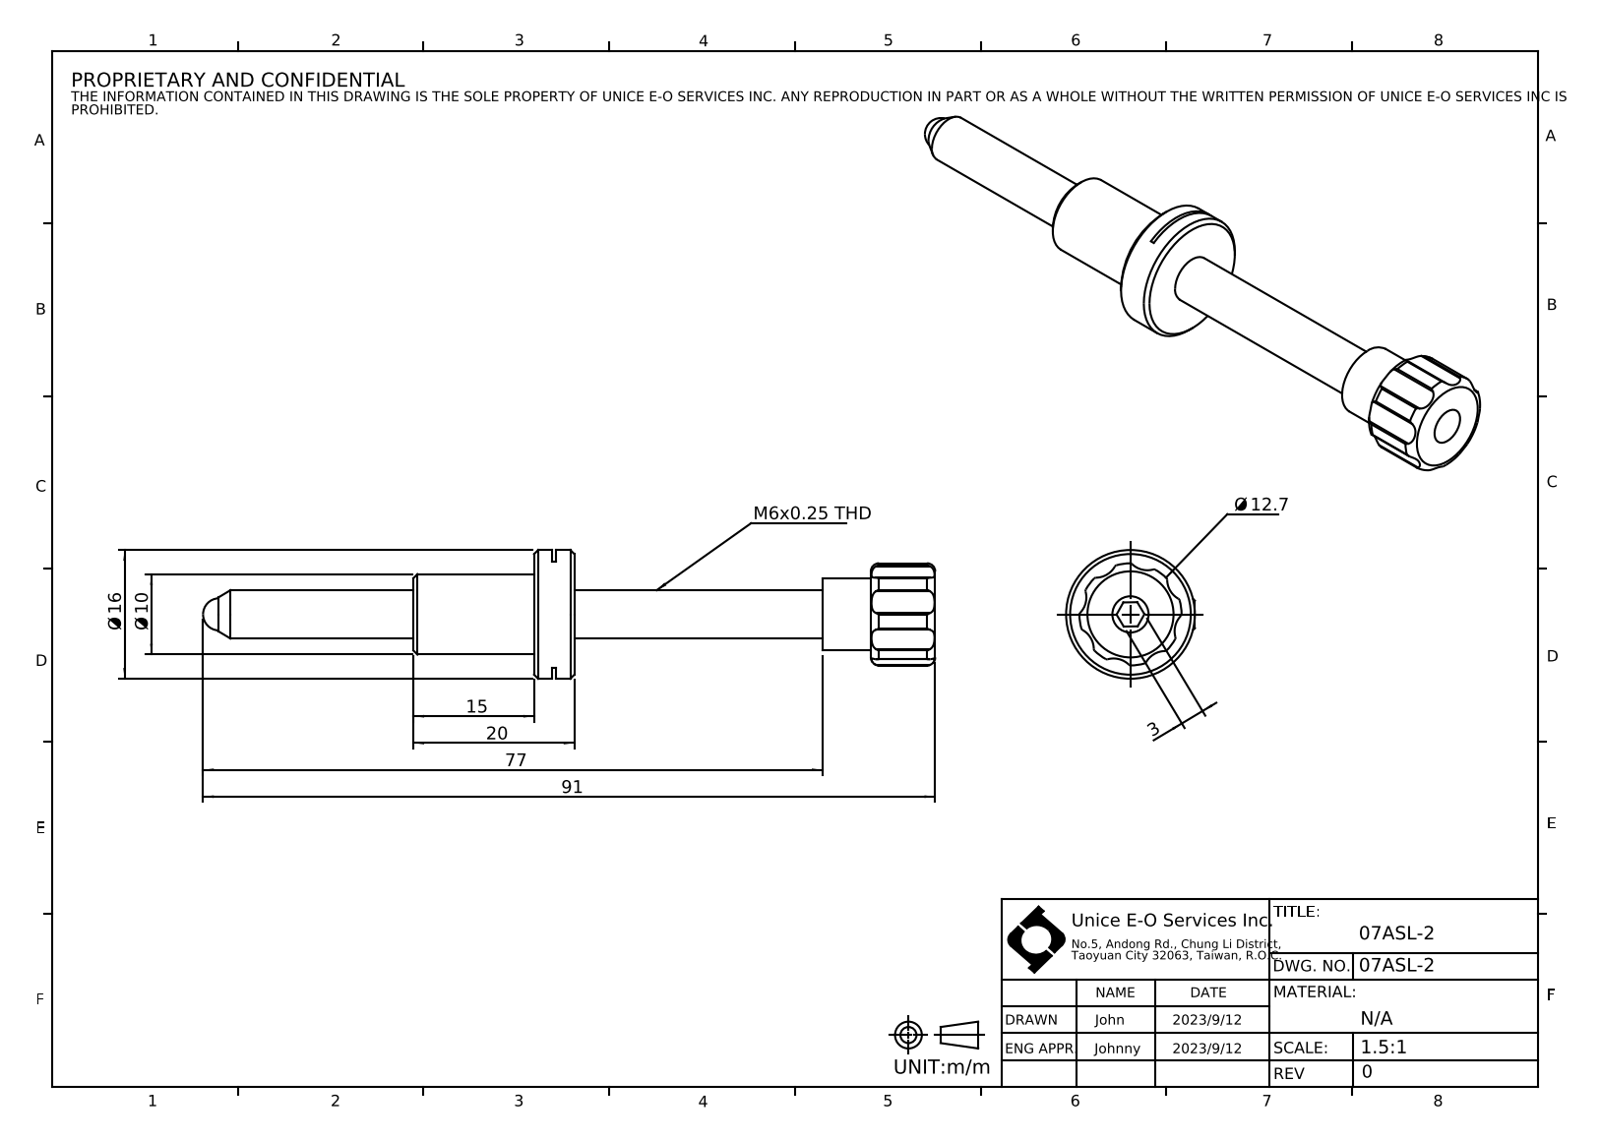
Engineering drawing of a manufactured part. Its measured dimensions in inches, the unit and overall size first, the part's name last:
Units: inches
Overall size (bounding box): 3.583 × 0.63 × 0.63
Round holes (diameter × count): ⌀0.177 ×1
Round bosses / shafts (diameter × count): ⌀0.63 ×1, ⌀0.394 ×1, ⌀0.354 ×1, ⌀0.236 ×1, ⌀0.157 ×1
Partial cylindrical surfaces — rounded edges, fillets, slot ends (radius × count): R0.012 ×16, R0.108 ×8, R0.25 ×1
Main face-to-face distances: 0.089, 0.108, 0.02, 0.197, 1.894, 1.805, 1.785, 1.697, 1.343, 1.254
Bodies: 0 solids, 80 faces (17 planar, 47 cylindrical, 16 other)
Part name (STEP PRODUCT): 07ASL-2
STEP written by: SolidWorks 2016 (AUTOMOTIVE_DESIGN)
